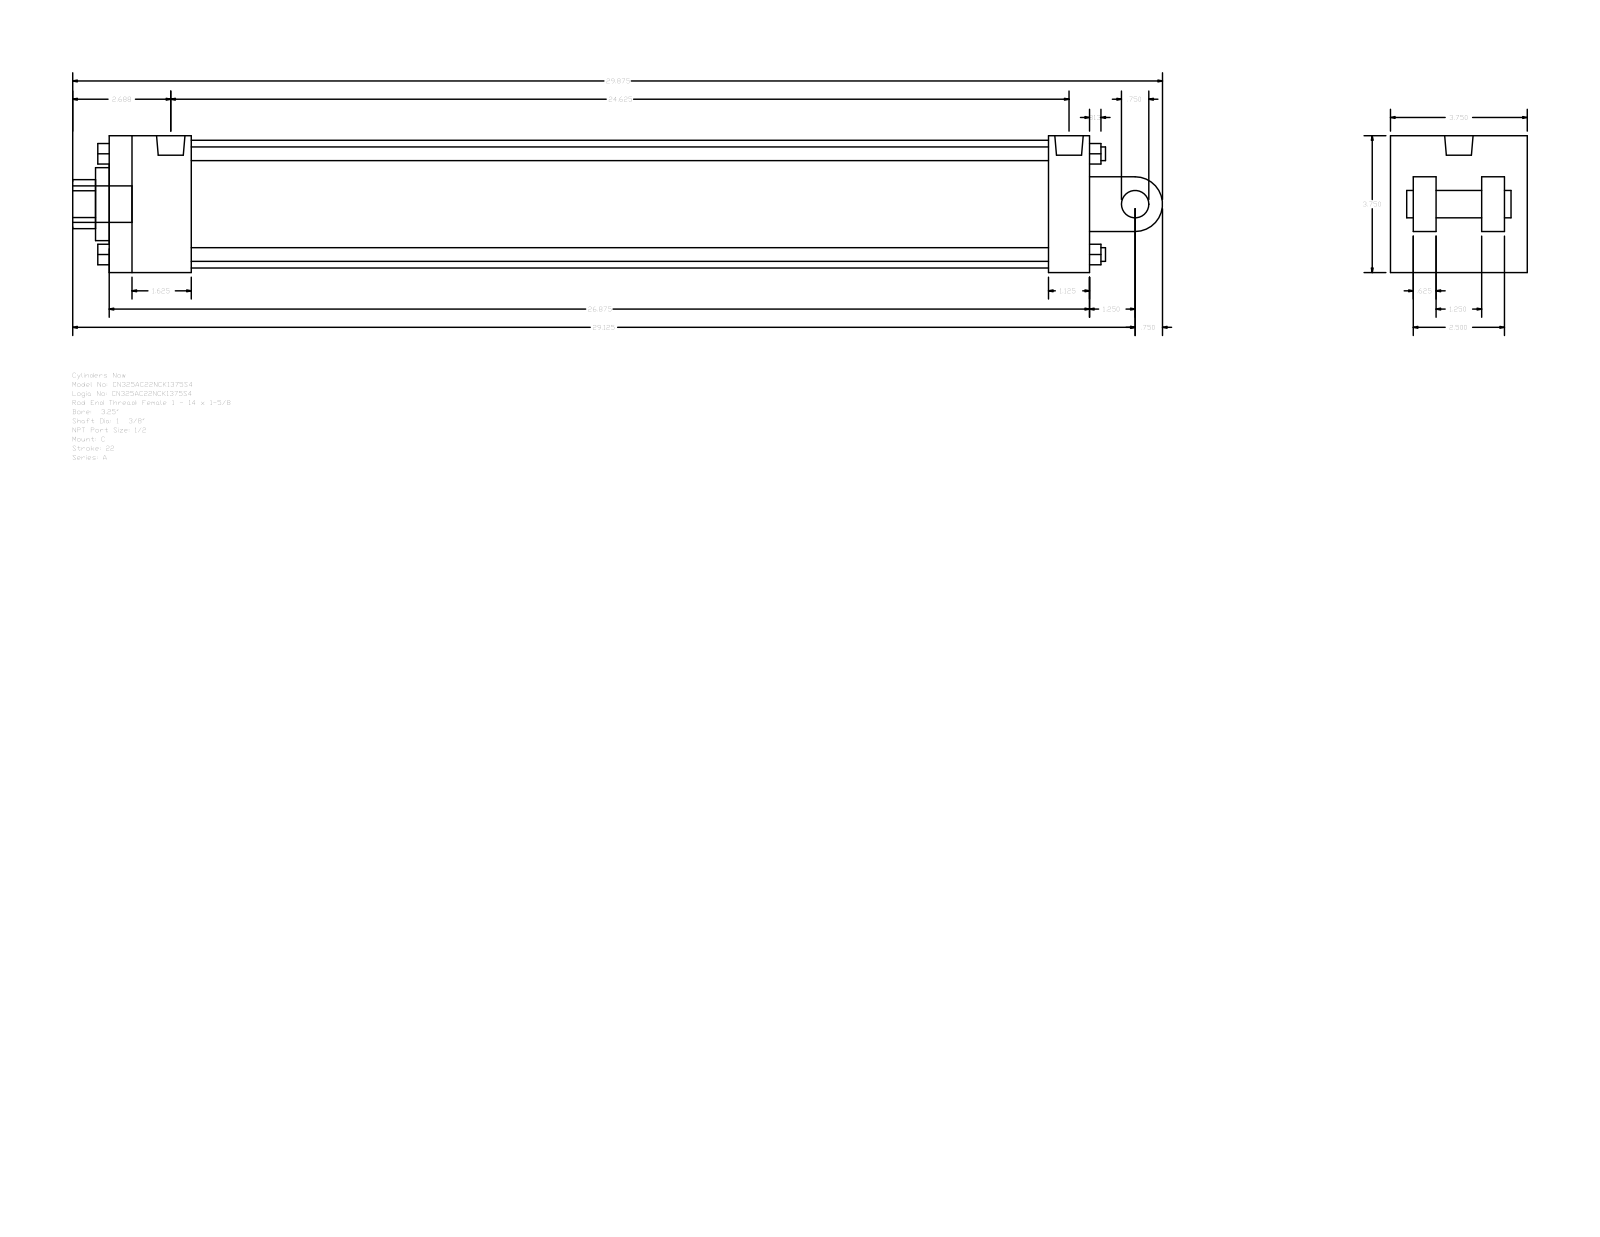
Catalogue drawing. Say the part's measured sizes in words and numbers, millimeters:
The part is named "A_C__0325_1.375". Its 3-D file was written by "GSSL Pune (CONFIG_CONTROL_DESIGN)". It is 0 solids with 135 faces: 102 planar, 33 cylindrical and 0 other. Overall it measures 758.83 by 95.25 by 95.25 millimeters. Round holes: 2 of diameter 8.73, 1 of diameter 19.77, 1 of diameter 34.92, 1 of diameter 50.8, 1 of diameter 88.9. Round bosses or shafts: 4 of diameter 9.53, 2 of diameter 8.73, 1 of diameter 25.4, 1 of diameter 19.77, 1 of diameter 19.05. Partial cylindrical surfaces (rounded edges, fillets, slot ends): 1 of radius 17.06, 1 of radius 19.05. The main face-to-face distances are 95.24, 15.87, 682.62, 28.57, 63.5, 66.67, 31.74, 79.37, 47.63, 654.05. The hole center spacings are 3.18.
